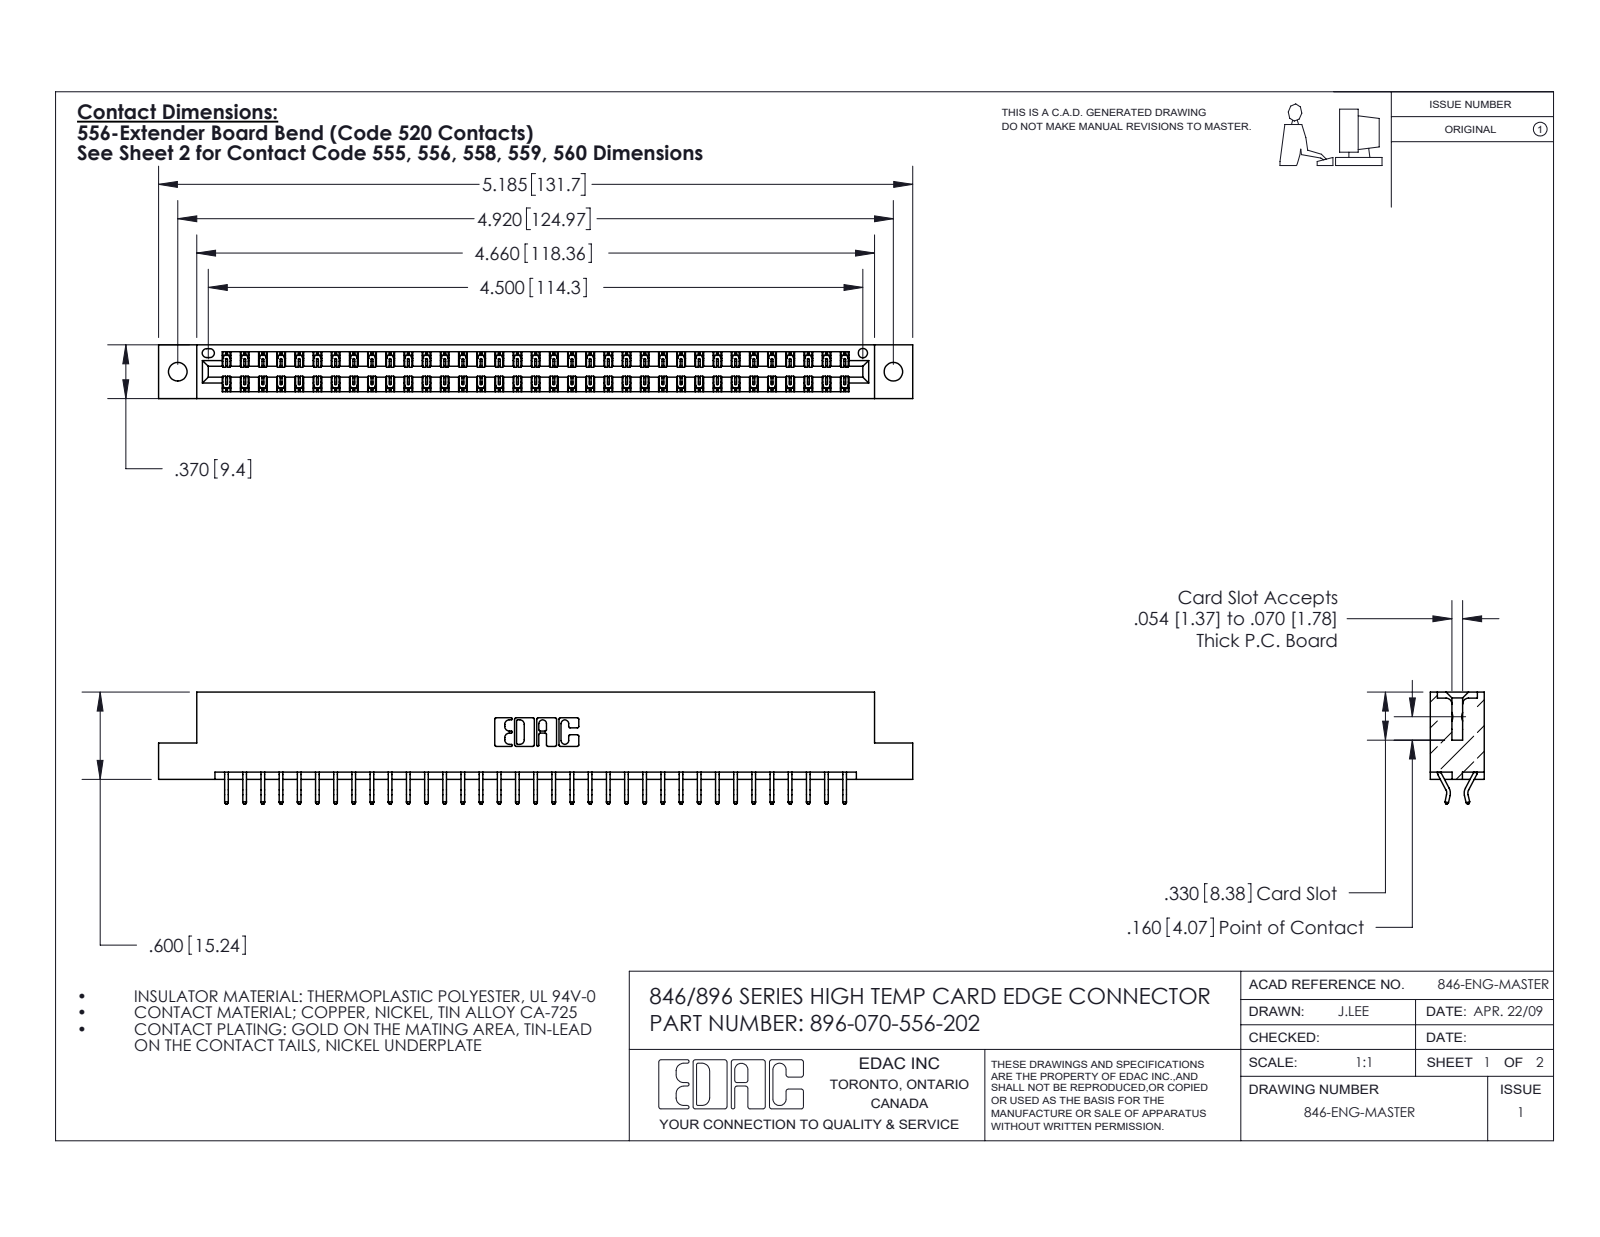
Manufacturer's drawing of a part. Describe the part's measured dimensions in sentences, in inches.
The part is named "345-292-001_556 Tail; 346 Part_Flush Mounting Lugs - 0.128 Dia; 396-070-556-202". Its 3-D file was written by "SolidWorks 2016 (CONFIG_CONTROL_DESIGN)". It is 71 solids with 4182 faces: 2806 planar, 1376 cylindrical and 0 other. Overall it measures 5.185 by 0.77 by 0.37 inches. Its volume is 0.778 cubic inches and its surface area 26.47 square inches. Round holes: 2 of diameter 0.128, 1 of diameter 0.064. Partial cylindrical surfaces (rounded edges, fillets, slot ends): 105 of radius 0.006, 22 of radius 0.01, 6 of radius 0.007, 6 of radius 0.031, 3 of radius 0.026, 2 of radius 0.01, 2 of radius 0.014, 2 of radius 0.022. The main face-to-face distances are 0.048, 0.322, 0.37, 0.25, 0.025, 0.072, 0.298, 0.275, 0.148, 0.222. The hole center spacings are 0.246, 4.711, 4.92.
